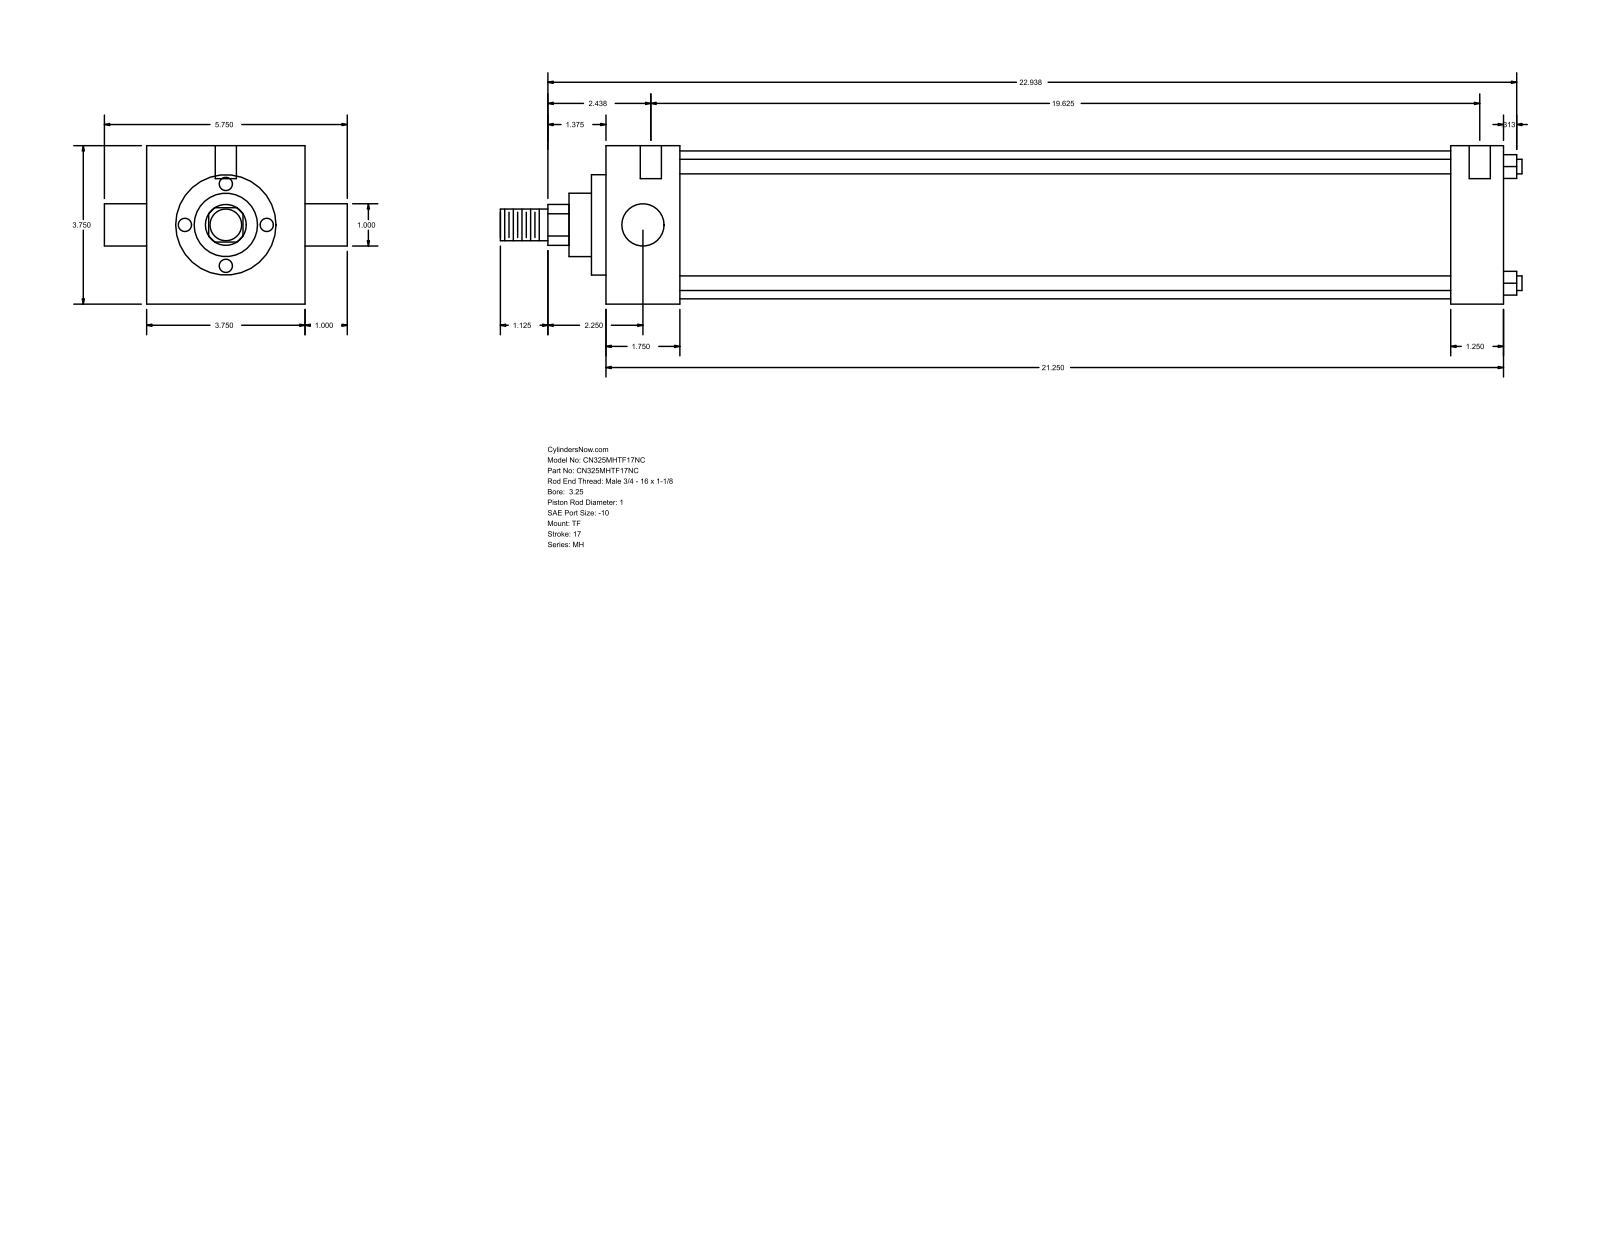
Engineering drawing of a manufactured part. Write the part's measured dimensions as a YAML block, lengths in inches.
part_name: "MH_TF__0325_1"
step_written_by: "GSSL Pune (CONFIG_CONTROL_DESIGN)"
units: inches
bodies: {solids: 0, faces: 86, planar: 61, cylindrical: 25, other: 0}
overall_size: [24.187, 5.75, 3.75]
round_holes:
  - {diameter: 0.219, count: 3}
  - {diameter: 0.5, count: 2}
round_bosses_or_shafts:
  - {diameter: 0.345, count: 4}
  - {diameter: 1, count: 2}
  - {diameter: 3.5, count: 1}
  - {diameter: 2.375, count: 1}
  - {diameter: 1.5, count: 1}
  - {diameter: 0.75, count: 1}
partial_cylinders:
  - {radius: 0.484, count: 1}
face_to_face_distances: [3.75, 21.25, 1.75, 20, 18.25, 19.5, 1.25, 0.344, 2.094, 20.344]
hole_center_spacings: [0.062, 0.187, 19.625, 19.687, 19.813, 19.875]
